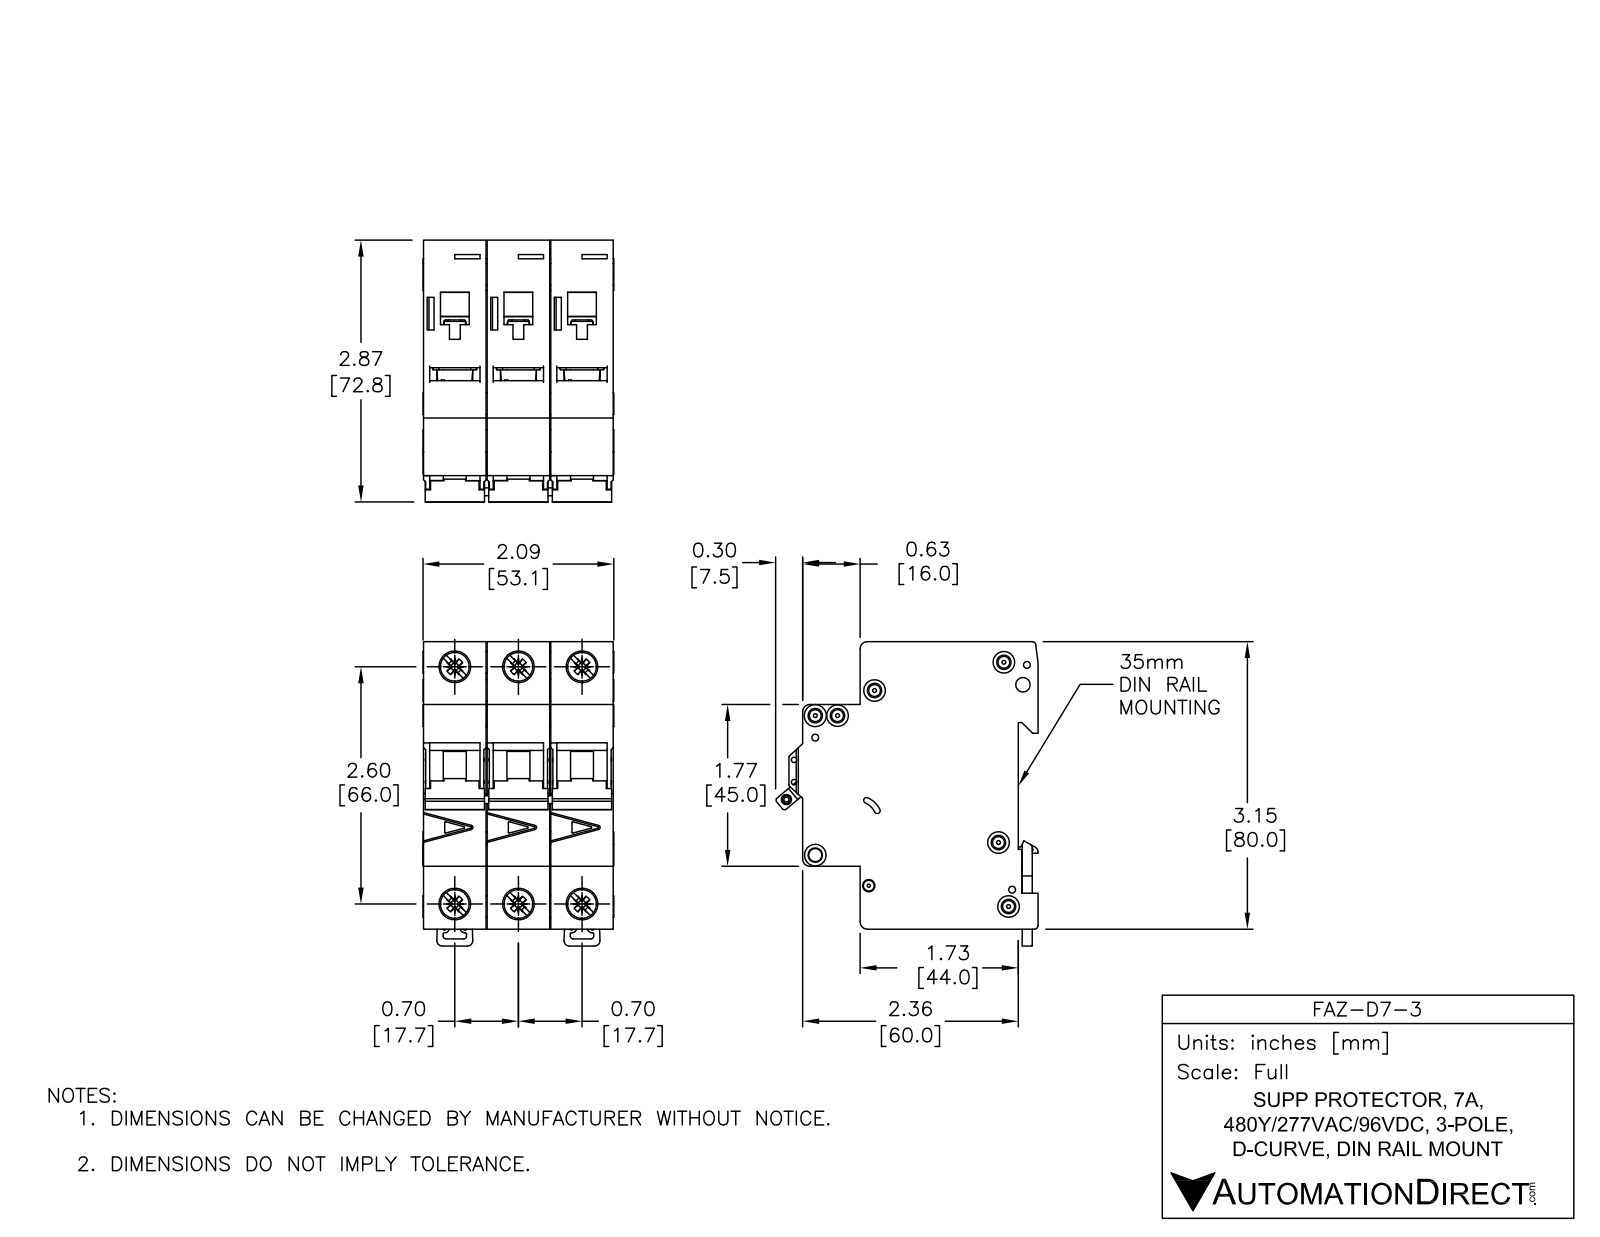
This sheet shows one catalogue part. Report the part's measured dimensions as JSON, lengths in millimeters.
{"part_name": "FAZ-D7-3", "step_written_by": "SolidWorks 2014 (AUTOMOTIVE_DESIGN)", "units": "millimeters", "bodies": {"solids": 11, "faces": 1650, "planar": 697, "cylindrical": 590, "other": 363}, "overall_size": [84.78, 73.04, 53.1], "volume_mm3": 224680, "surface_area_mm2": 58052, "round_holes": [[3.6, 6], [8.2, 4], [1.9, 3], [1.09, 2], [1.5, 2], [4, 2], [7.15, 2], [2.15, 1], [2.2, 1], [2.55, 1], [3.3, 1], [3.4, 1]], "round_bosses_or_shafts": [[6, 4], [2.5, 3], [8.2, 2]], "partial_cylinders_radius": [[0.25, 68], [0.5, 25], [1, 12], [2, 12], [0.2, 11], [1.8, 3], [0.8, 2], [3, 2]], "face_to_face_distances": [17.7, 17.5, 35.4, 35.2, 52.9, 17.9, 79.48, 5.5, 49.5, 44], "hole_center_spacings": [17.7, 68.33, 66, 6.2, 13.64, 35.4, 74.89, 4.81]}
